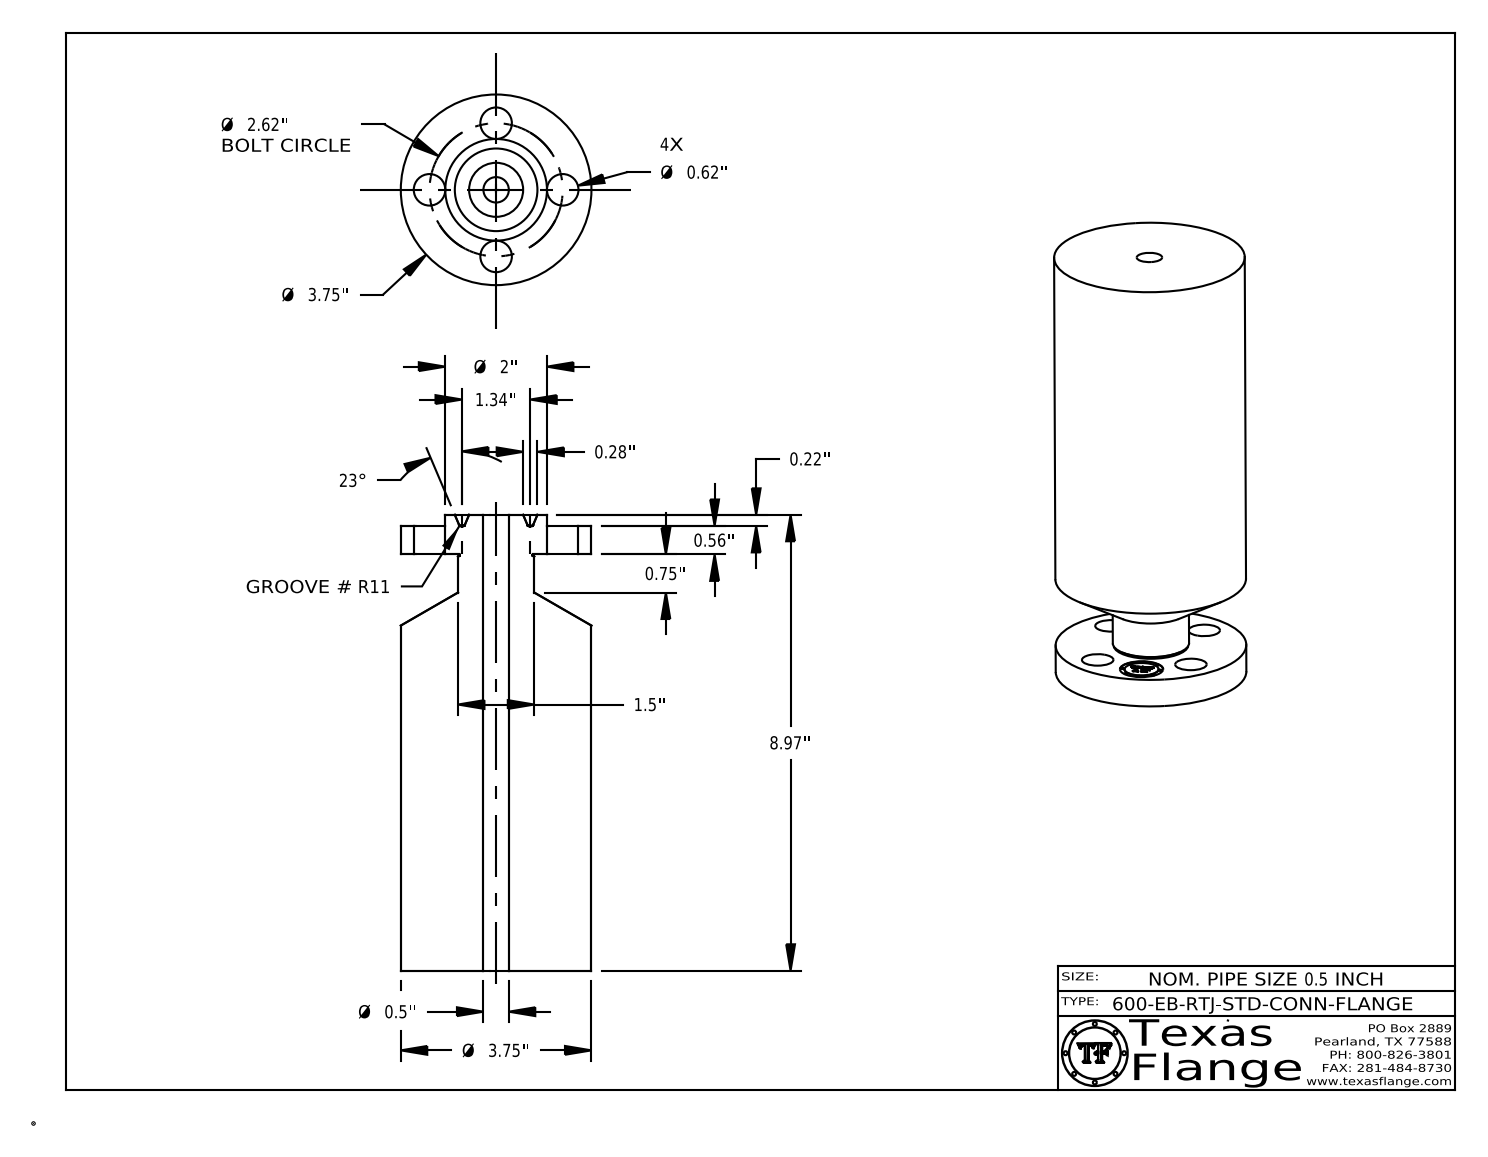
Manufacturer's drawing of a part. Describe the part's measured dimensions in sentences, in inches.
The part is named "0.5-600-EB-RTJ-STD-CONN-FLANGE". Its 3-D file was written by "CATIA V5 STEP AP214 (AUTOMOTIVE_DESIGN)". It is 1 solid with 423 faces: 371 planar, 38 cylindrical and 14 other. Overall it measures 8.969 by 3.75 by 3.75 inches. Its volume is 84.31 cubic inches and its surface area 150.6 square inches. Round holes: 4 of diameter 0.62, 1 of diameter 0.5, 1 of diameter 0.85. Round bosses or shafts: 8 of diameter 0.051, 1 of diameter 3.75, 1 of diameter 2, 1 of diameter 1.5, 1 of diameter 0.67. The main face-to-face distances are 8.19, 0.56, 8.75, 0.219, 0.779, 8.969, 0.774, 0.555, 8.195, 0.254. The hole center spacings are 1.31, 1.852, 1.003, 2.42, 2.62, 1.31.
